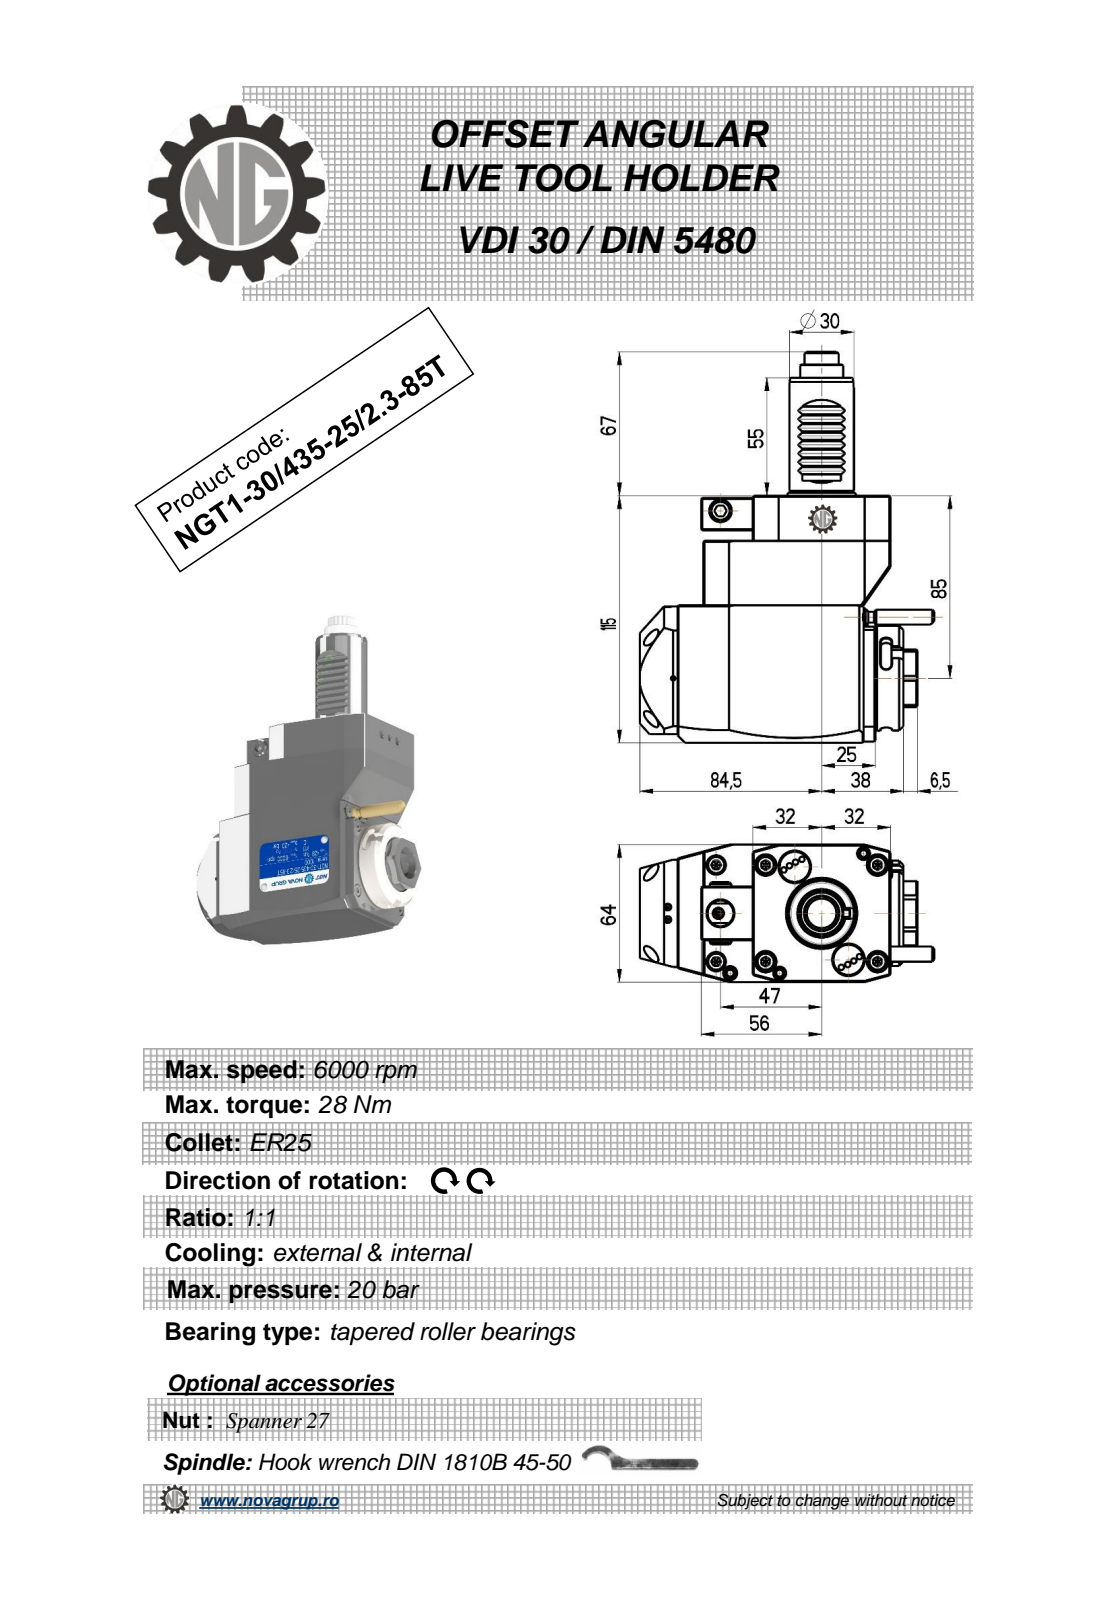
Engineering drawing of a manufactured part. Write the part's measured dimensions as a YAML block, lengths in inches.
part_name: "NGT1_30_435_25_1_3_85T"
step_written_by: "PRO/ENGINEER BY PARAMETRIC TECHNOLOGY CORPORATION, 2010280 (CONFIG_CONTROL_DESIGN)"
units: inches
bodies: {solids: 1, faces: 458, planar: 219, cylindrical: 149, other: 90}
overall_size: [7.165, 5.389, 2.52]
volume: 43.61
surface_area: 94.19
round_holes:
  - {diameter: 0.098, count: 1}
  - {diameter: 0.118, count: 1}
  - {diameter: 0.374, count: 1}
  - {diameter: 0.472, count: 1}
  - {diameter: 0.709, count: 1}
round_bosses_or_shafts:
  - {diameter: 0.315, count: 2}
  - {diameter: 1.929, count: 1}
  - {diameter: 1.654, count: 1}
  - {diameter: 1.181, count: 1}
  - {diameter: 0.787, count: 1}
  - {diameter: 0.394, count: 1}
  - {diameter: 0.276, count: 1}
  - {diameter: 0.197, count: 1}
partial_cylinders:
  - {radius: 0.078, count: 36}
  - {radius: 0.012, count: 16}
  - {radius: 0.098, count: 6}
  - {radius: 7.087, count: 2}
  - {radius: 0.167, count: 1}
  - {radius: 0.177, count: 1}
  - {radius: 0.279, count: 1}
  - {radius: 0.312, count: 1}
face_to_face_distances: [2.52, 4.528, 0.276, 3.701, 3.15, 3.425, 0.236, 1.161, 0.512, 0.827]
hole_center_spacings: [1.348, 2.032, 3.012]
